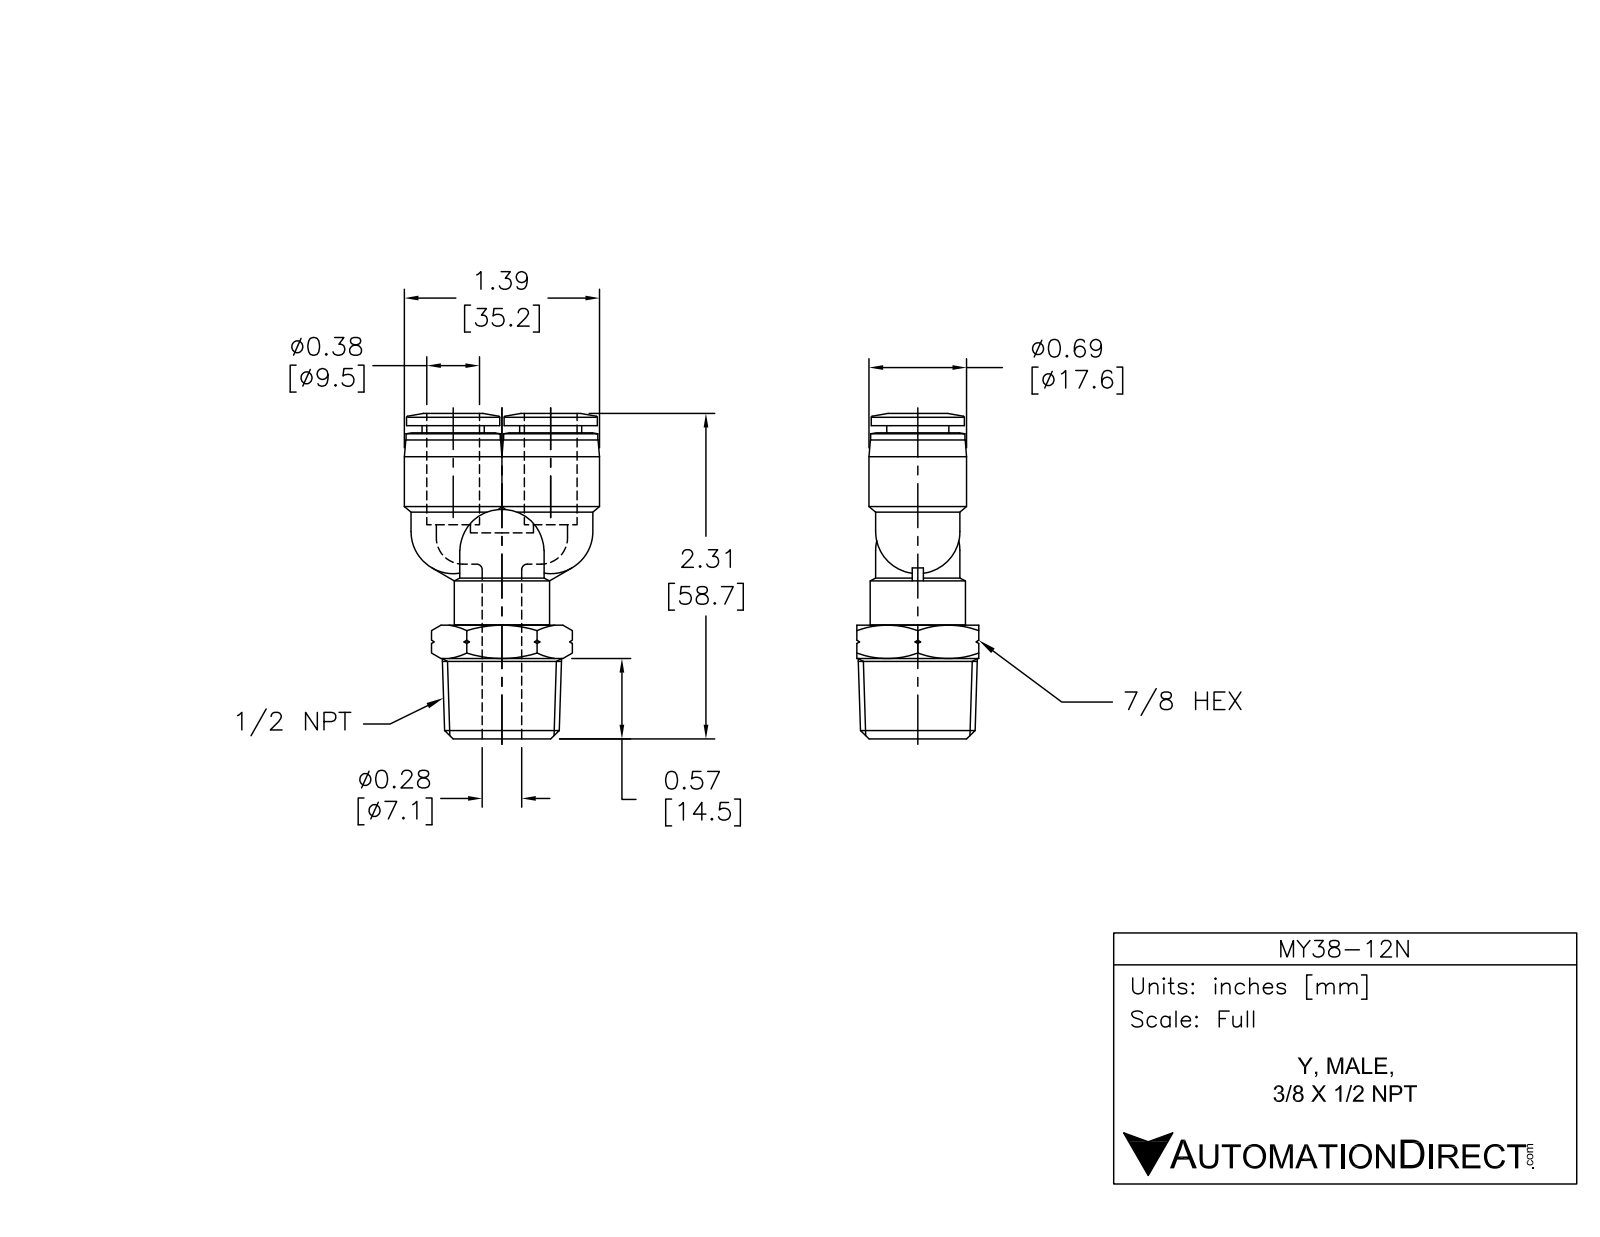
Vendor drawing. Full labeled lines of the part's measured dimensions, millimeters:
Part name (STEP PRODUCT): MY38-12N
STEP written by: SolidWorks 2015 (AUTOMOTIVE_DESIGN)
Units: millimetres
Bodies: 1 solid, 126 faces (22 planar, 32 cylindrical, 72 other)
Overall size (bounding box): 58.7 × 35.2 × 22
Volume: 16 800 mm³ · Surface area: 8 394 mm²
Round holes (diameter × count): ⌀9.8 ×2, ⌀7 ×1
Round bosses / shafts (diameter × count): ⌀15.2 ×3, ⌀17.6 ×2, ⌀17 ×2, ⌀16.8 ×2, ⌀11.2 ×2, ⌀17.2 ×1
Main face-to-face distances: 56.5, 22, 1.3, 55.2, 18, 20.5, 34.7, 36, 38.5, 16.7
Hole centre spacings: 8.8, 17.6
